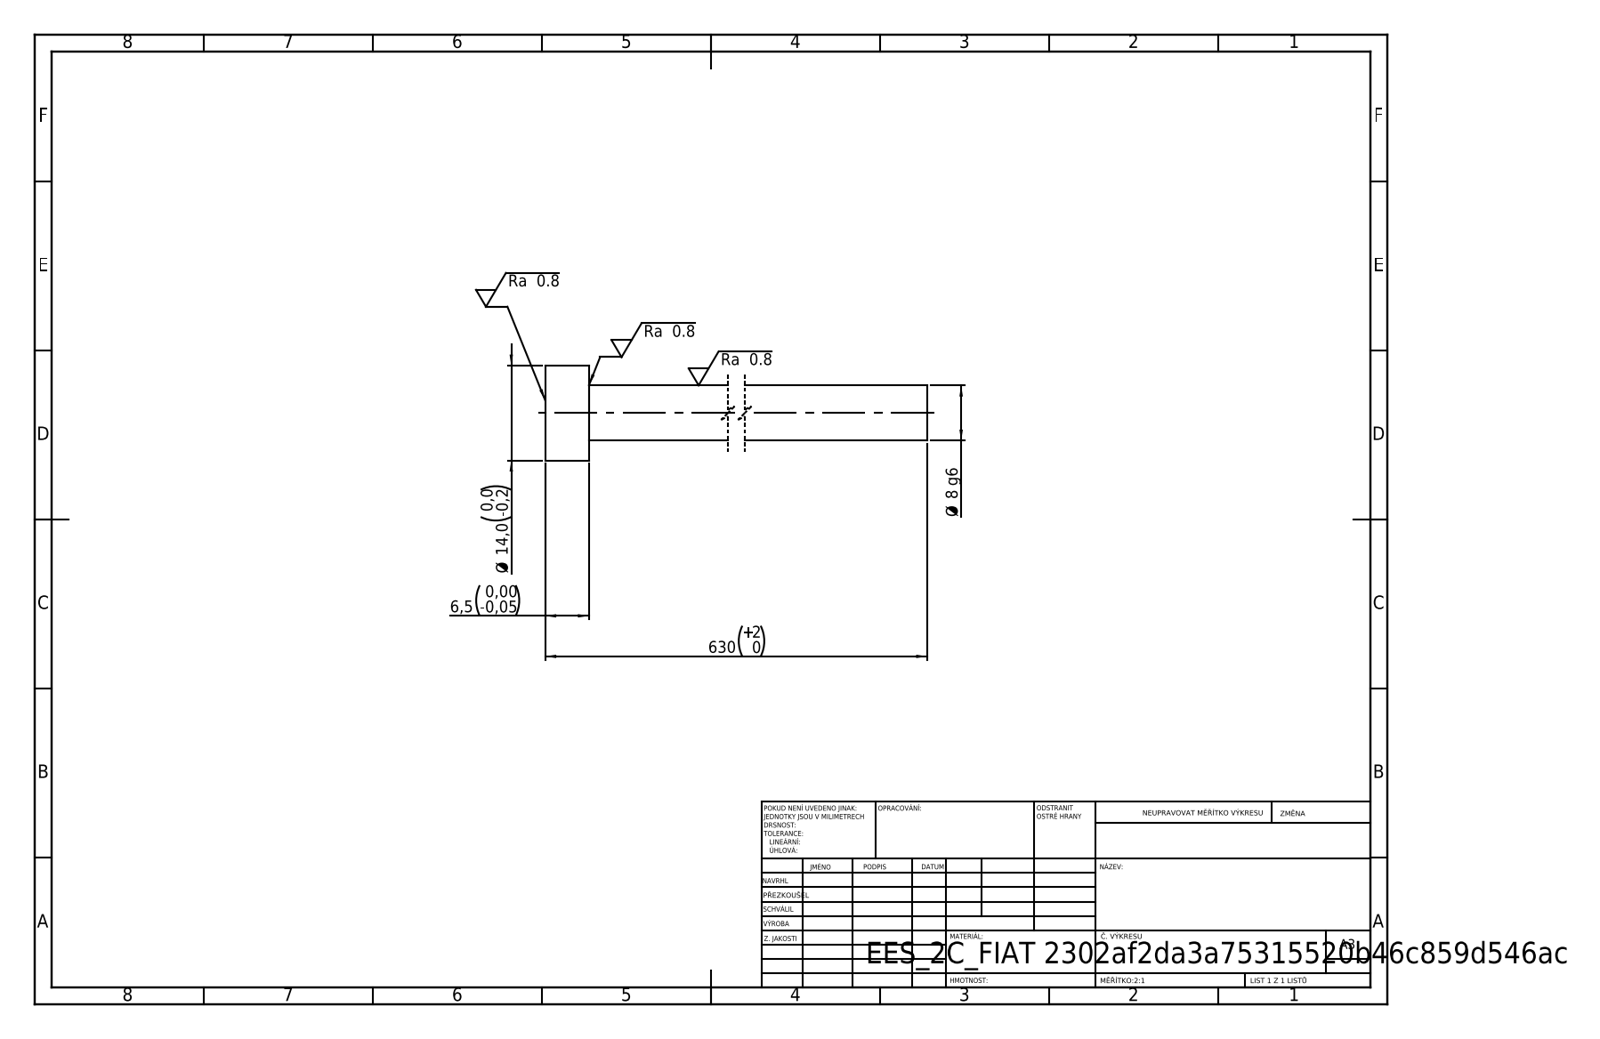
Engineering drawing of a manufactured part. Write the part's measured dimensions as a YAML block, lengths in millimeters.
step_written_by: "SolidWorks 2019 (CONFIG_CONTROL_DESIGN)"
units: millimeters
bodies: {solids: 1, faces: 7, planar: 3, cylindrical: 4, other: 0}
overall_size: [630, 14, 14]
volume: 33928
surface_area: 16656
round_bosses_or_shafts:
  - {diameter: 14, count: 1}
  - {diameter: 8.2, count: 1}
face_to_face_distances: [6.5, 630, 623.5]
